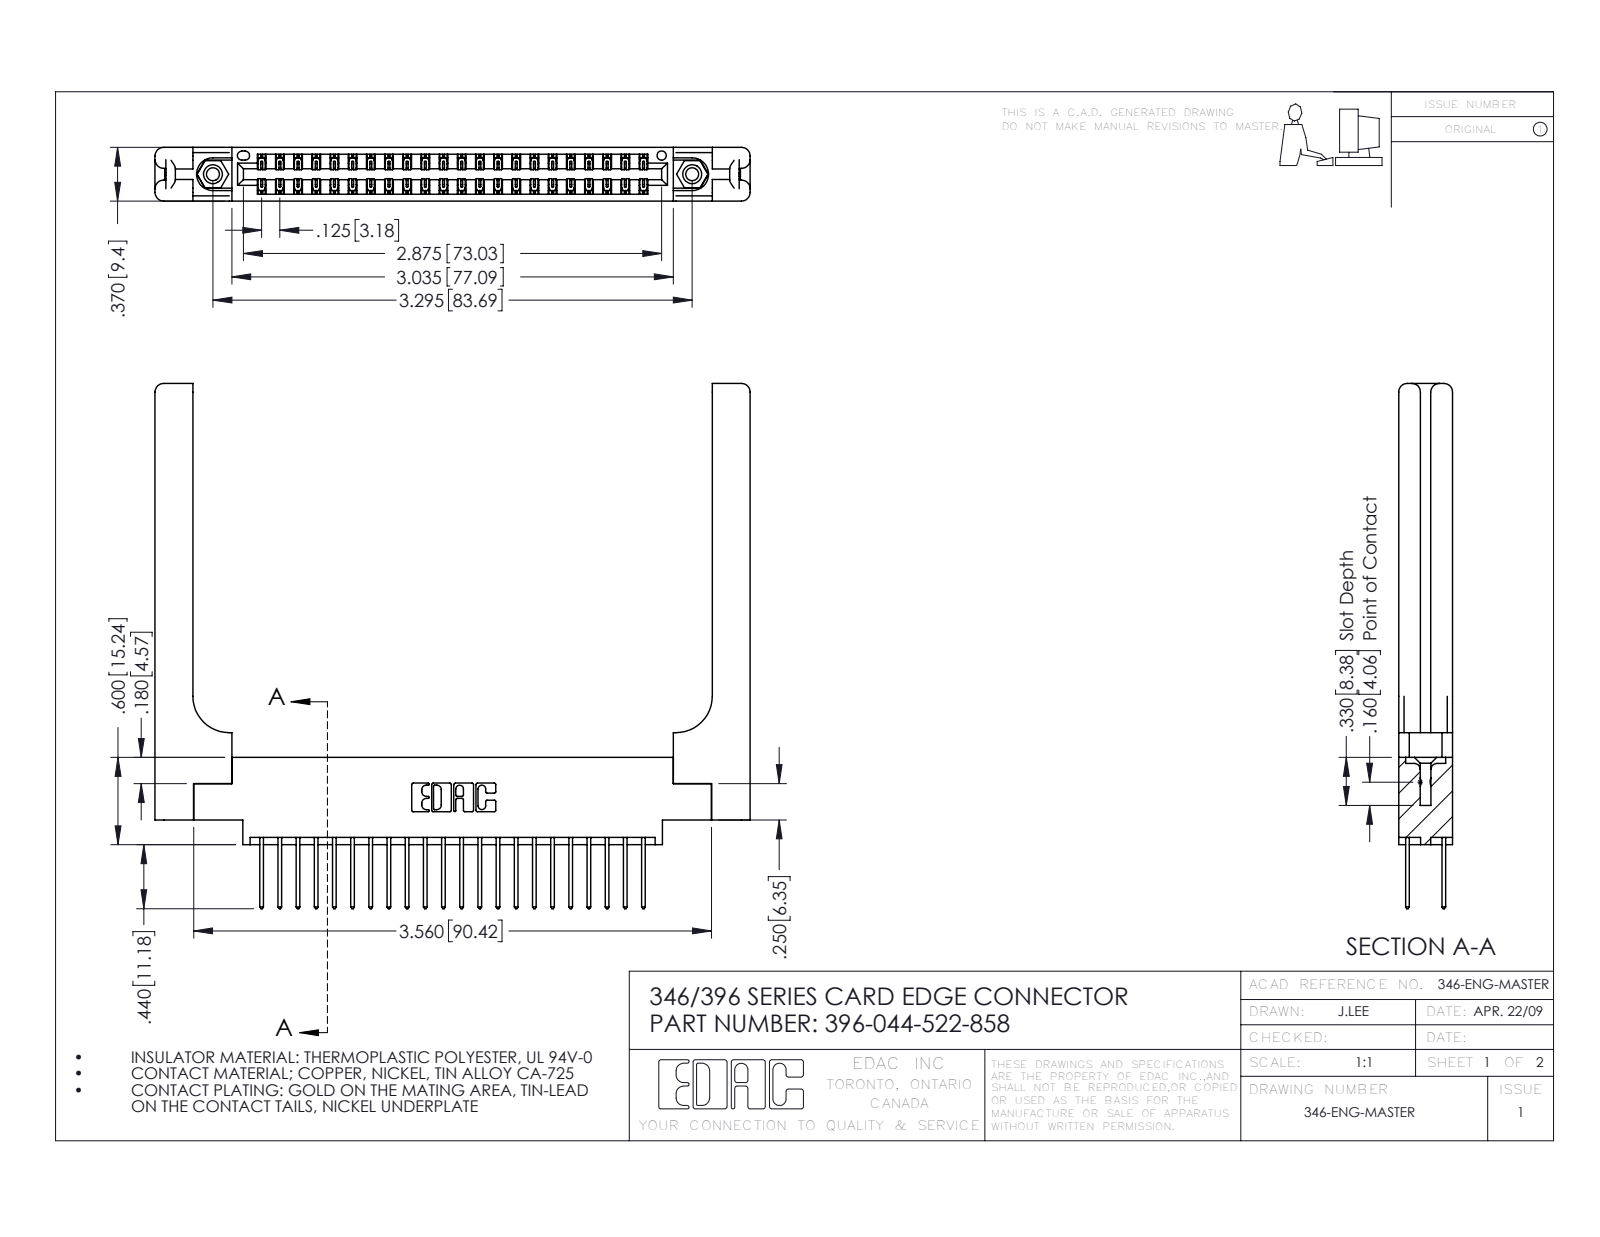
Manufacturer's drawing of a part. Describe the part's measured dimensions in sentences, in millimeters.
The part is named "346-220-058_345-220-058; 345-292-001_345-293-122; 345-250-001_345-250-001-102; 346 Part_0.170 Offset - 0.156 Dia-TH (+1 more)". Its 3-D file was written by "SolidWorks 2016 (CONFIG_CONTROL_DESIGN)". It is 49 solids with 2670 faces: 1768 planar, 842 cylindrical and 60 other. Overall it measures 103.9 by 91.7 by 9.4 millimeters. Its volume is 17 440 cubic millimeters and its surface area 19 020 square millimeters. Round holes: 2 of diameter 2.3, 2 of diameter 3.2, 2 of diameter 4, 1 of diameter 1.6. Round bosses or shafts: 2 of diameter 3.9. Partial cylindrical surfaces (rounded edges, fillets, slot ends): 66 of radius 0.2, 44 of radius 0.3, 22 of radius 0.3, 16 of radius 1.5, 6 of radius 0.2, 6 of radius 0.8, 3 of radius 0.7, 2 of radius 0.4. The main face-to-face distances are 9.4, 1.8, 1.2, 8.2, 3.8, 3.8, 6.4, 0.6, 7.6, 7. The hole center spacings are 6.2, 78.4, 83.7.
